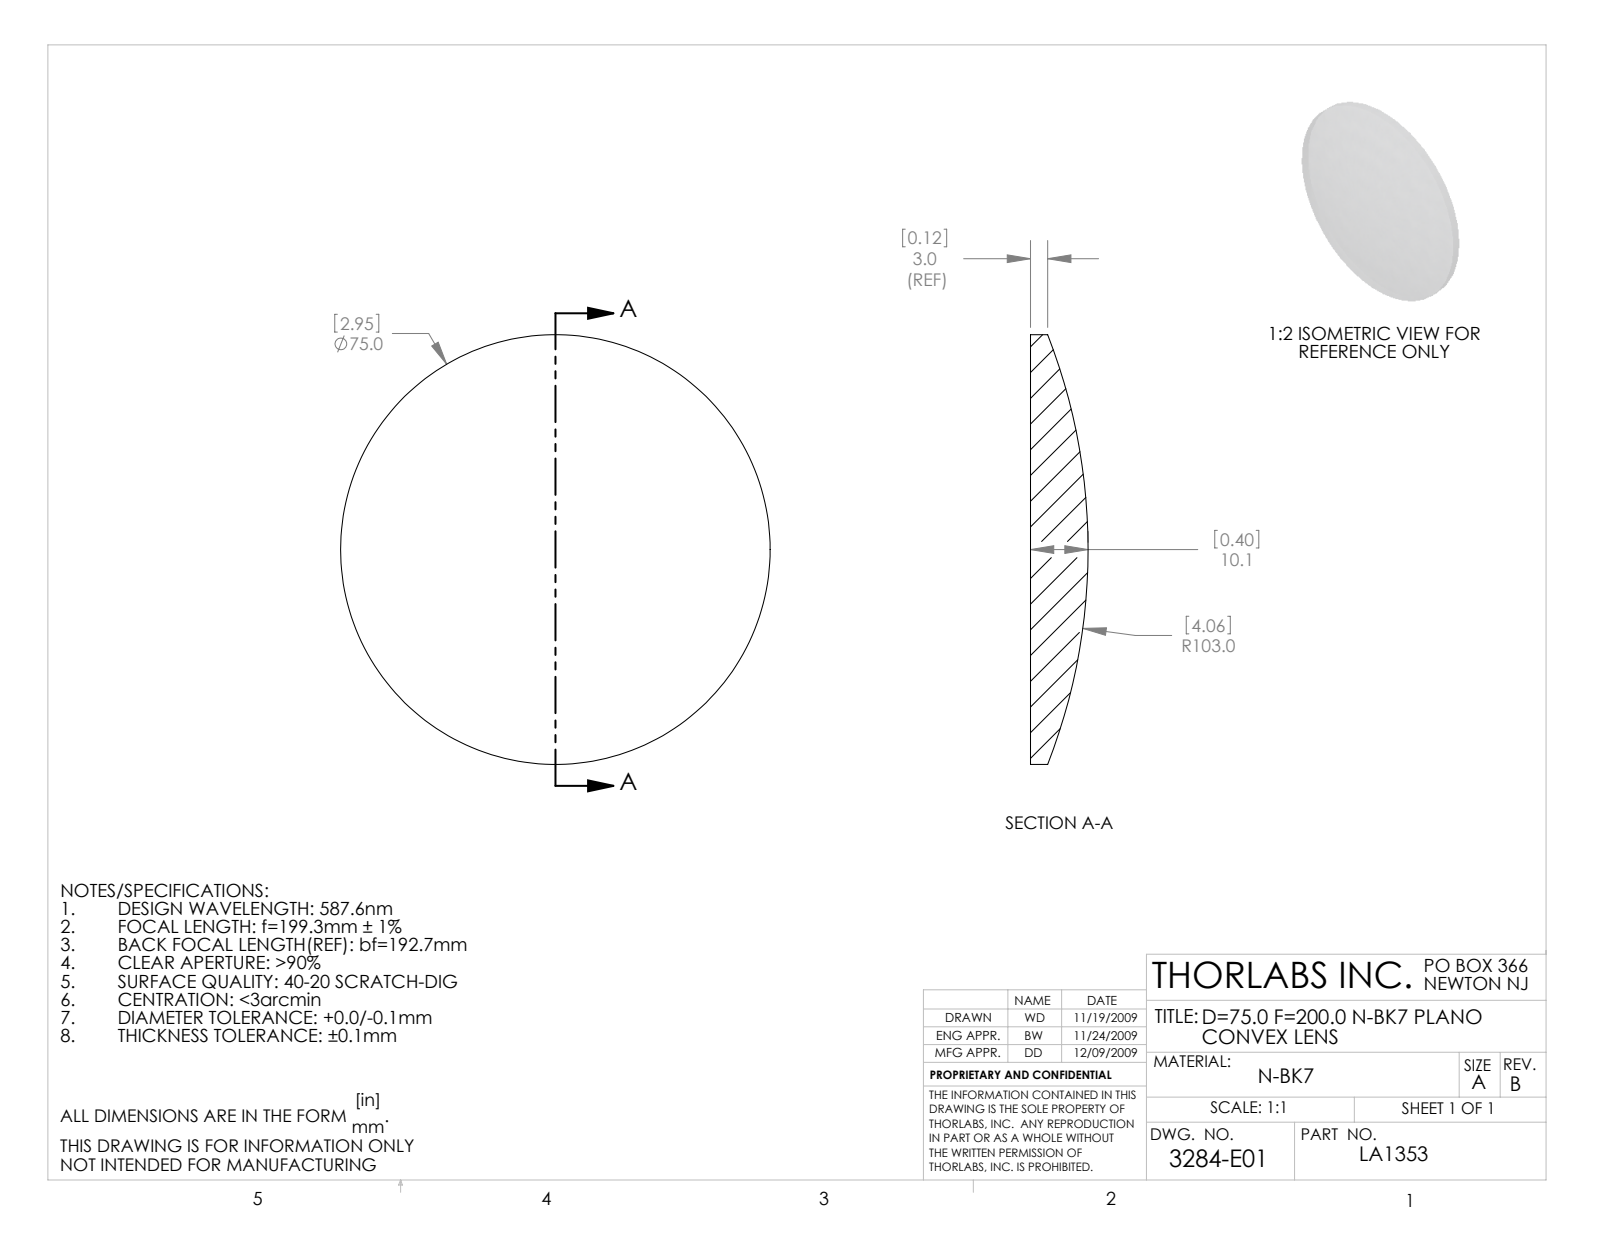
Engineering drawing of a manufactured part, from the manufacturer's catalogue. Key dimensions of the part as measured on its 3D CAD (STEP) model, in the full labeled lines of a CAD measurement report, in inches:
Part name (STEP PRODUCT): 3284-E0W
STEP written by: SolidWorks 2009 (AUTOMOTIVE_DESIGN)
Units: inches
Bodies: 1 solid, 5 faces (1 planar, 2 cylindrical, 2 other)
Overall size (bounding box): 2.953 × 2.953 × 0.396
Volume: 1.771 in³ · Surface area: 15.03 in²
Round bosses / shafts (diameter × count): ⌀2.953 ×1
